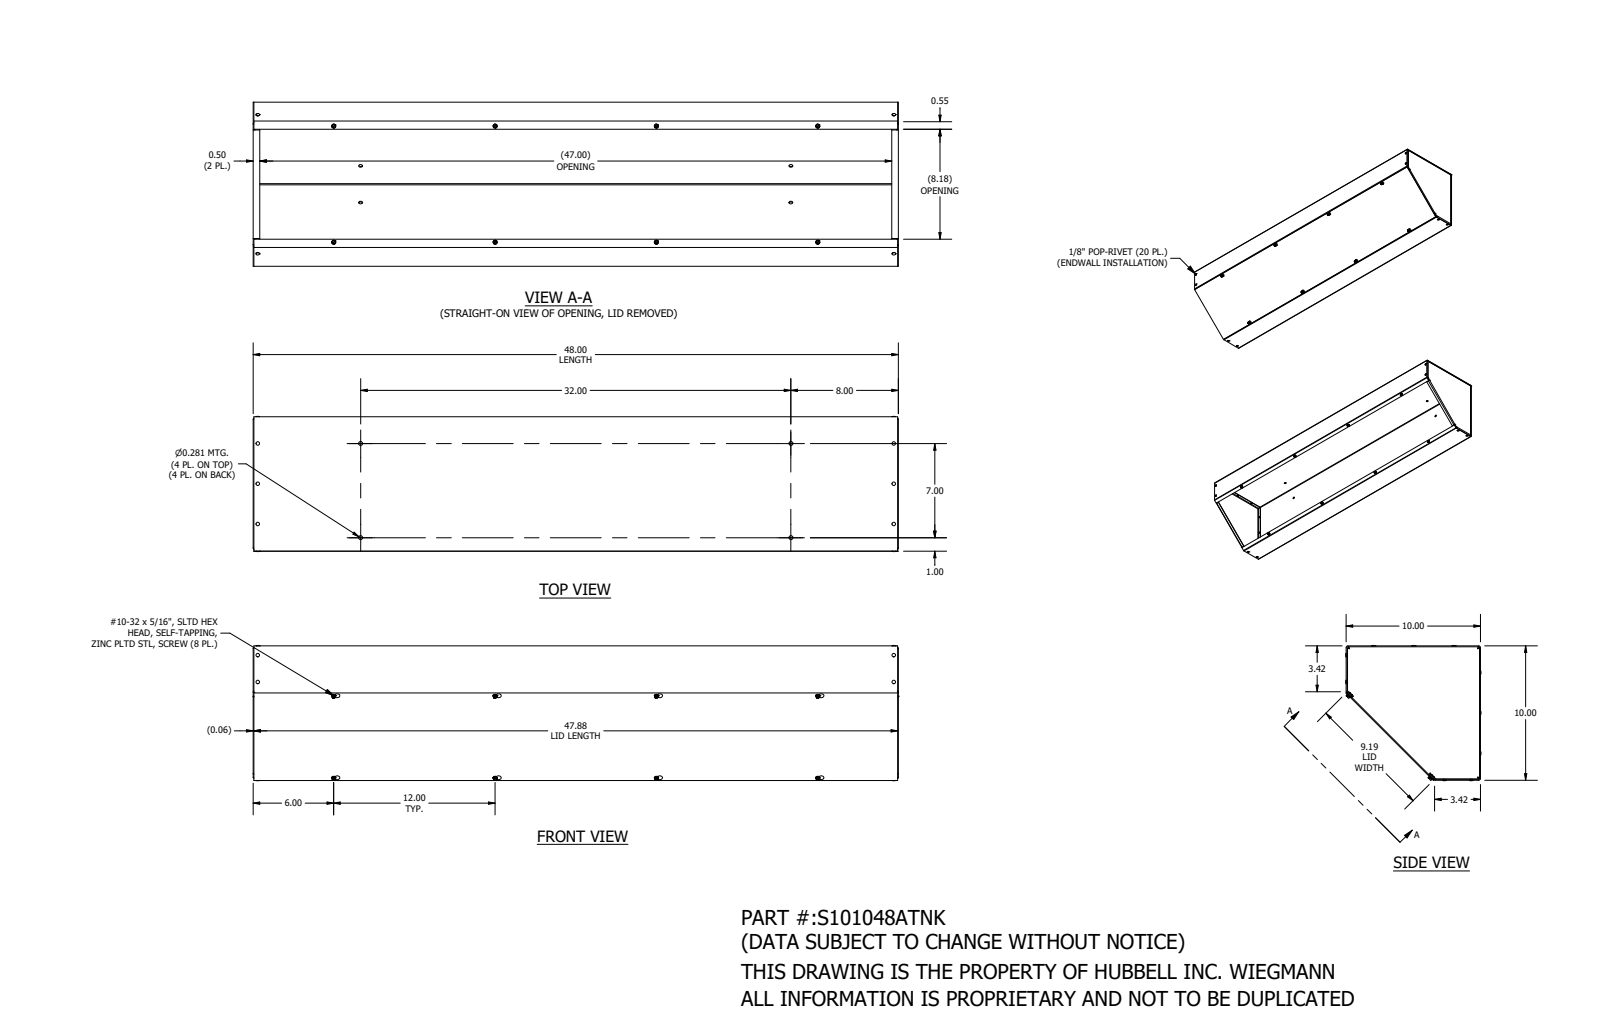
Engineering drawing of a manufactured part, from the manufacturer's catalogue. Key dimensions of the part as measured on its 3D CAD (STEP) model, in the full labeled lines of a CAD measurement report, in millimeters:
Part name (STEP PRODUCT): S101048ATNK
STEP written by: SolidWorks 2021 (AUTOMOTIVE_DESIGN)
Units: millimetres
Bodies: 32 solids, 1724 faces (396 planar, 472 cylindrical, 856 other)
Overall size (bounding box): 1219.2 × 256 × 256
Volume: 2 348 000 mm³ · Surface area: 2 520 000 mm²
Round holes (diameter × count): ⌀3.3 ×20, ⌀4.3 ×8, ⌀7.1 ×8, ⌀10.3 ×8
Round bosses / shafts (diameter × count): ⌀6.7 ×20, ⌀3.2 ×11, ⌀3.2 ×9, ⌀8 ×8, ⌀4.6 ×8
Partial cylindrical surfaces — rounded edges, fillets, slot ends (radius × count): R1.6 ×40, R3.5 ×15, R1.6 ×9, R2.8 ×8, R1.6 ×6
Main face-to-face distances: 1.9, 252.1, 250.2, 254, 1217.3, 1.7, 1219.2, 1215.4, 3.6, 3.8
Hole centre spacings: 304.8, 1201.8, 6.4, 76.2, 609.6, 1204.1, 298.5, 311.2
